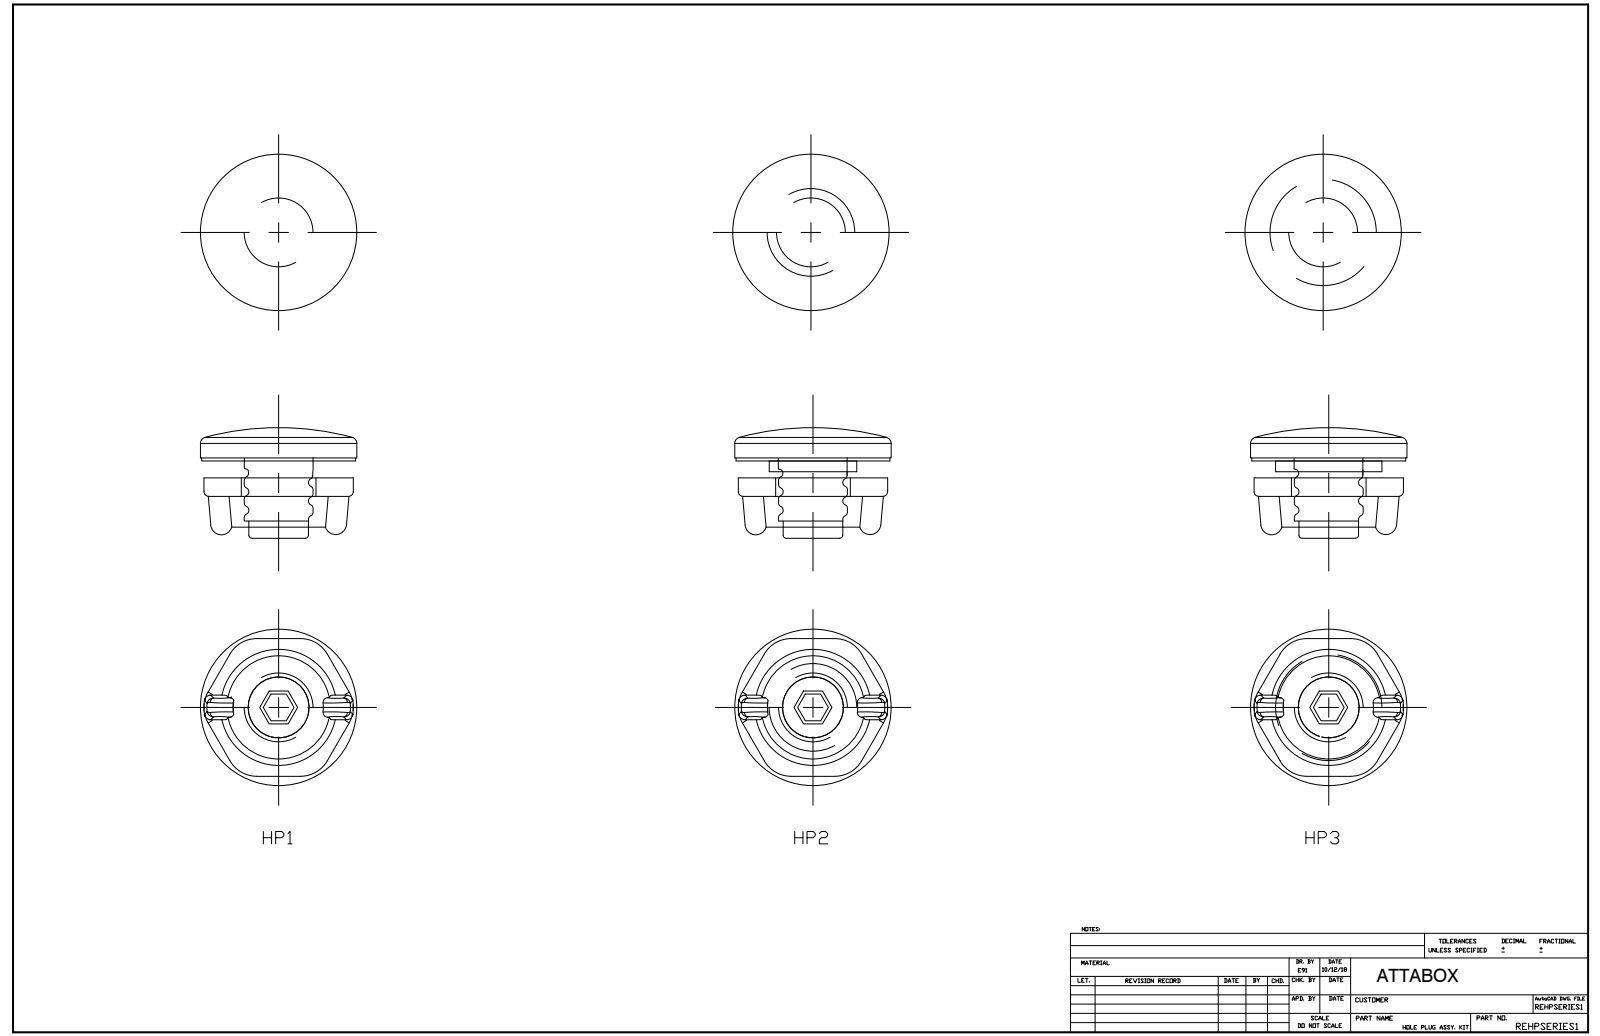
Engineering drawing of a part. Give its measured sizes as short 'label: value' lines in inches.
name: HPSERIES1
written by: SolidWorks 2018 (AUTOMOTIVE_DESIGN)
unit: in
bodies: 3 solids, 135 faces (32 planar, 49 cylindrical, 54 other)
size: 1 × 1 × 0.753
volume: 0.332 in³; area: 6.823 in²
holes: 1× ⌀0.44, 1× ⌀0.45
bosses: 1× ⌀1, 1× ⌀0.98, 1× ⌀0.38
rounds: 14× R0.03, 12× R0.01, 8× R0.08, 6× R0.196, 2× R0.061, 1× R0.02
face distances: 0.089, 0.125, 0.214, 0.2, 0.12, 0.245, 0.334, 0.19, 0.31, 0.435
